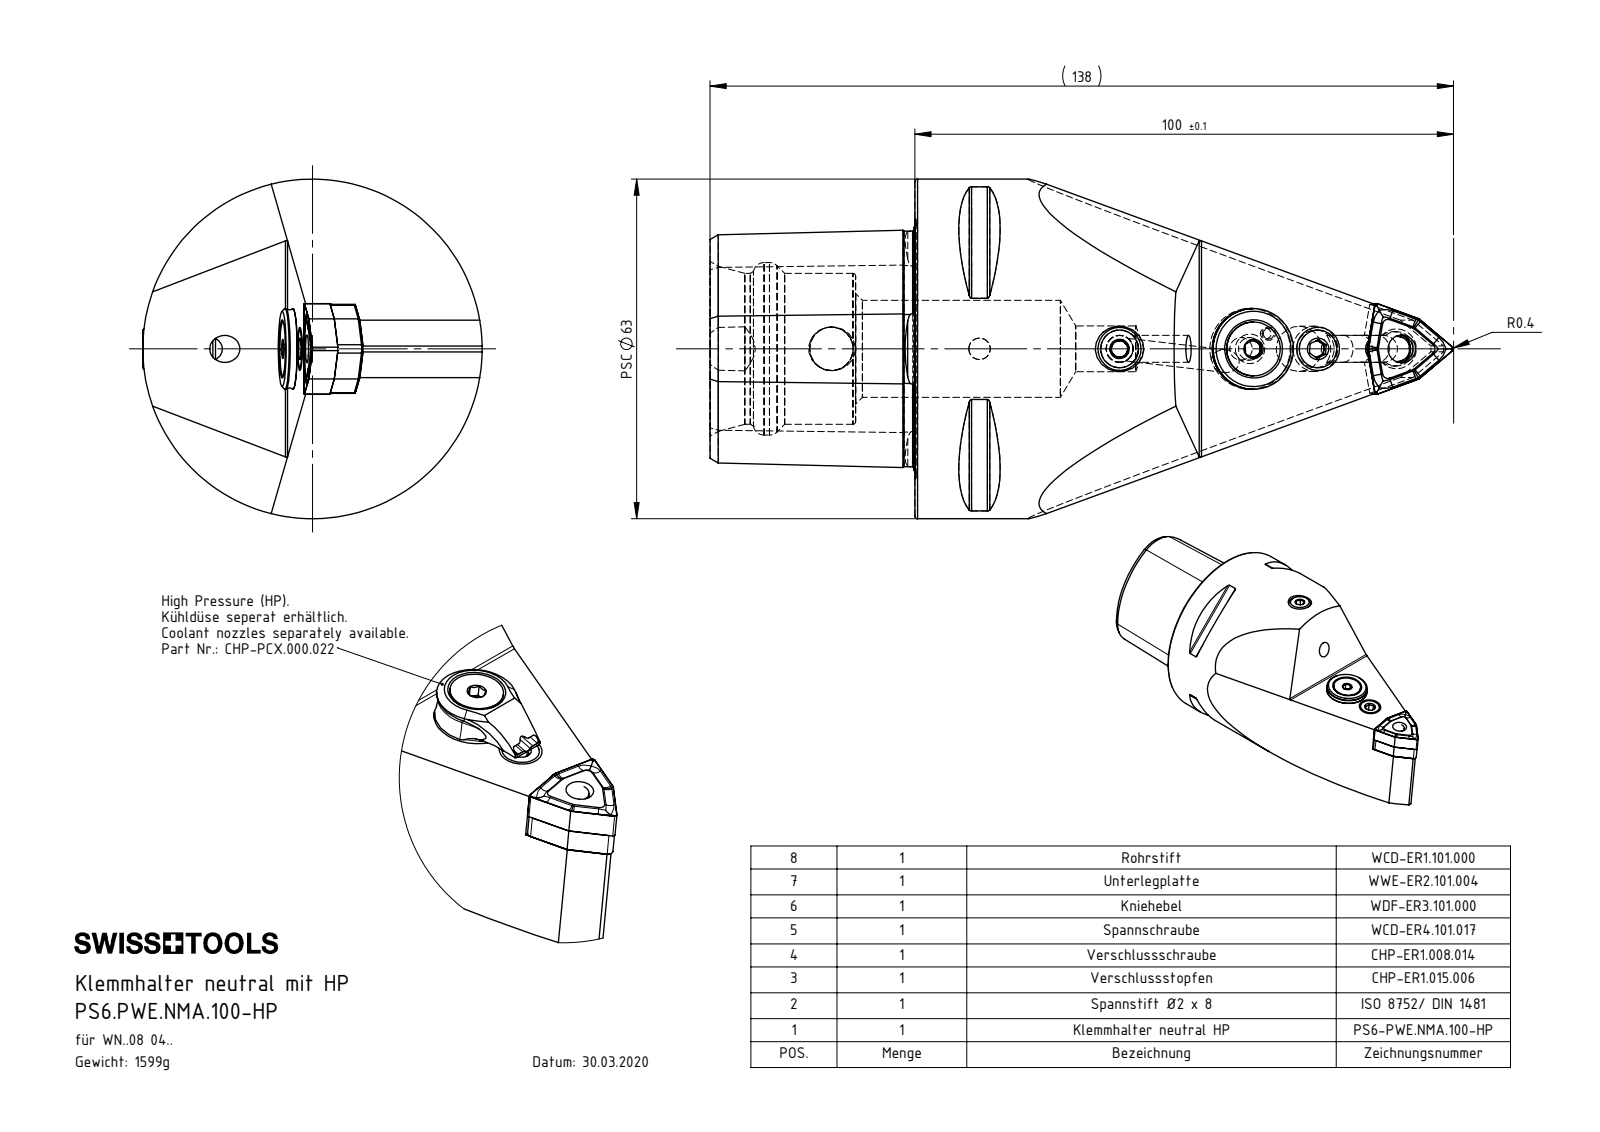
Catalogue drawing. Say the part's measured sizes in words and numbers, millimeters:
The part is named "CHP-ER1.015.006; WCD-ER4.101.017_A; PS6.PWE.NMA.100-HP; WCD-ER1.101.000 (+8 more)". Its 3-D file was written by "SolidWorks 2017 (AUTOMOTIVE_DESIGN)". It is 11 solids with 333 faces: 137 planar, 66 cylindrical and 130 other. Overall it measures 138 by 63 by 63 millimeters. Its volume is 203 417 cubic millimeters and its surface area 36 294 square millimeters. Round holes: 2 of diameter 4.2, 2 of diameter 5, 2 of diameter 7, 1 of diameter 1.2, 1 of diameter 2, 1 of diameter 2.5, 1 of diameter 3, 1 of diameter 4, 1 of diameter 5.16, 1 of diameter 5.2, 1 of diameter 6.7, 1 of diameter 7.8. Round bosses or shafts: 2 of diameter 8, 1 of diameter 63, 1 of diameter 15, 1 of diameter 13.4, 1 of diameter 10, 1 of diameter 7.9, 1 of diameter 6.4, 1 of diameter 5.5. Partial cylindrical surfaces (rounded edges, fillets, slot ends): 9 of radius 0.5, 3 of radius 0.4, 3 of radius 1, 3 of radius 2.5, 1 of radius 2.3, 1 of radius 2.35, 1 of radius 2.8, 1 of radius 3.1. The main face-to-face distances are 38, 24.88, 4.47, 4.53, 27, 11, 4.7, 55.8, 4.76, 4.85. The hole center spacings are 4.51, 4.49, 4.53, 9.14, 9.17, 12.22, 12.25, 15.61.
